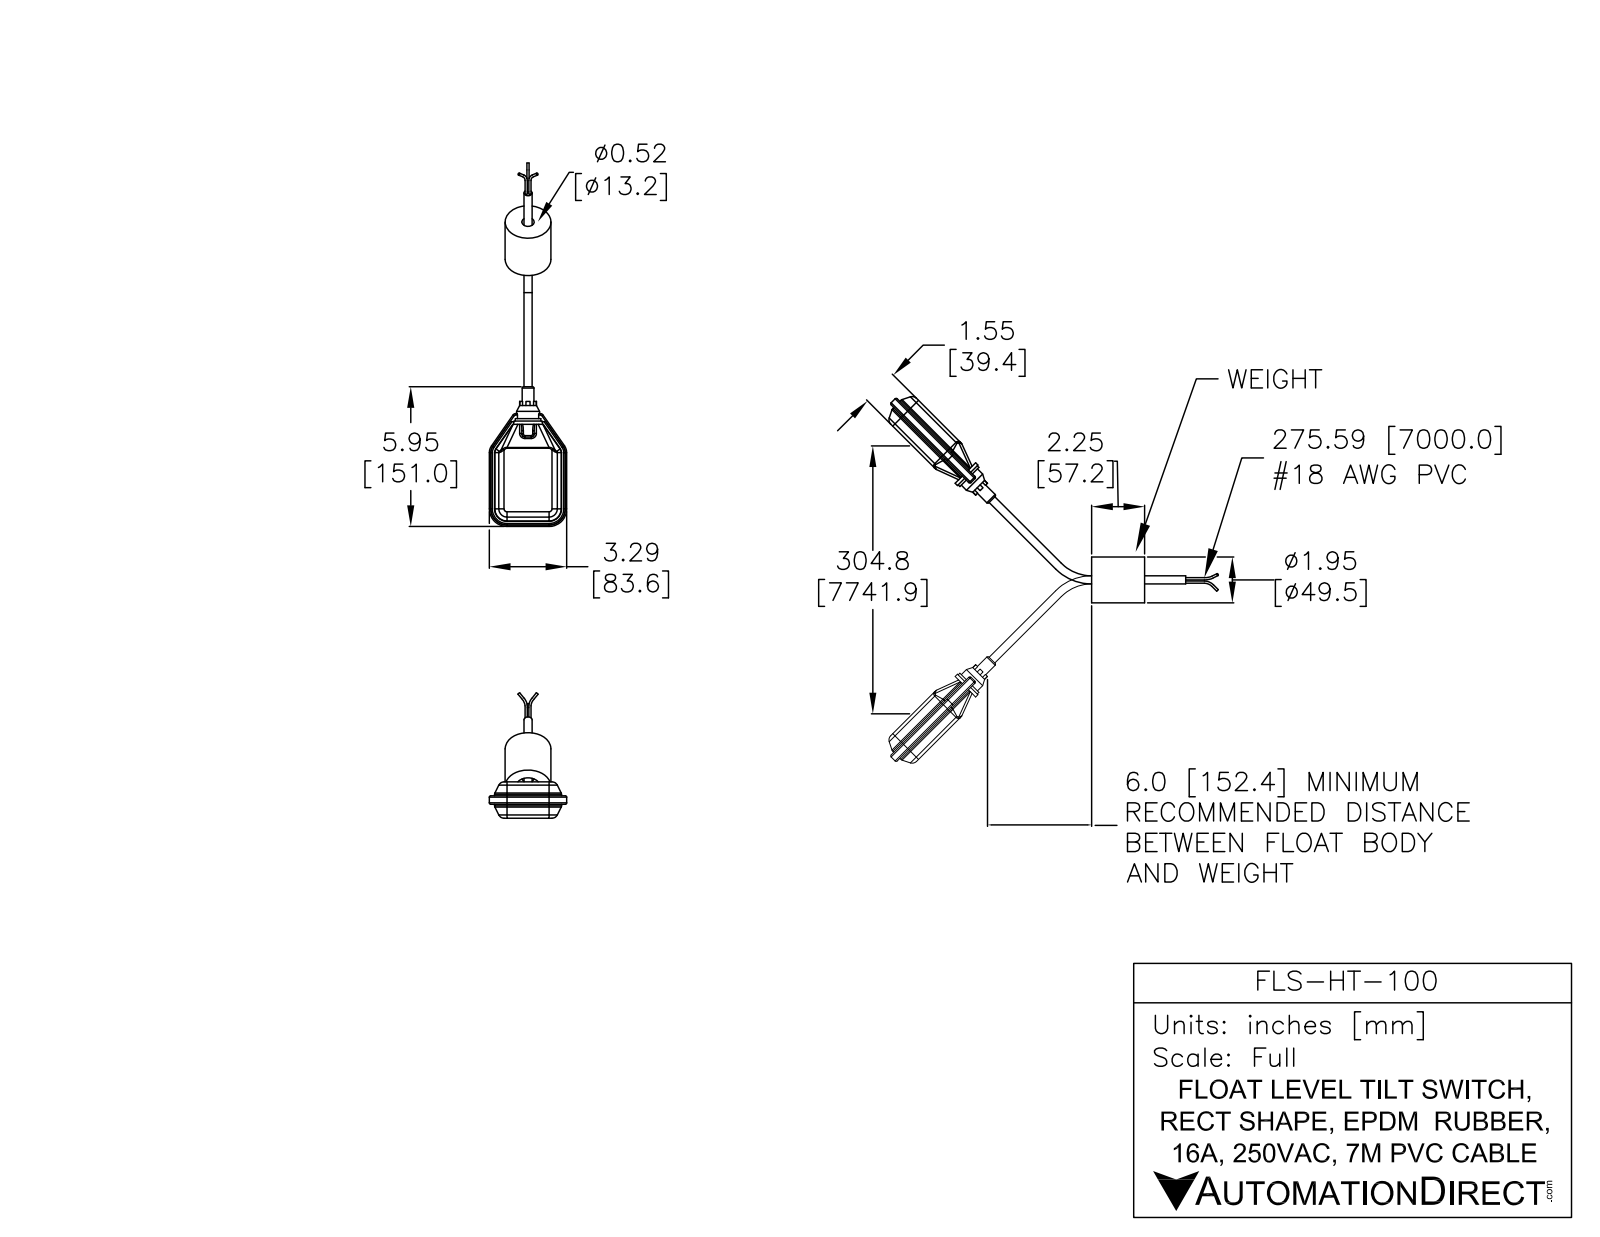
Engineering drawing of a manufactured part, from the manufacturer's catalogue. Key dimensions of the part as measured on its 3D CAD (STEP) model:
Part name (STEP PRODUCT): FLS-HT-100
STEP written by: SolidWorks 2013 (AUTOMOTIVE_DESIGN)
Units: inches
Bodies: 4 solids, 228 faces (59 planar, 79 cylindrical, 90 other)
Overall size (bounding box): 6.15 × 3.308 × 1.55
Volume: 18.8 in³ · Surface area: 53.51 in²
Round bosses / shafts (diameter × count): ⌀1.22 ×1, ⌀1.15 ×1, ⌀1 ×1, ⌀0.5 ×1
Partial cylindrical surfaces — rounded edges, fillets, slot ends (radius × count): R0.05 ×12, R0.062 ×10, R0.7 ×10, R0.04 ×8, R0.175 ×8, R0.125 ×6, R0.063 ×4, R0.5 ×2
Main face-to-face distances: 1.55, 3.105, 0.594, 0.956, 0.1, 0.14, 0.24, 0.125, 3.183, 0.362
